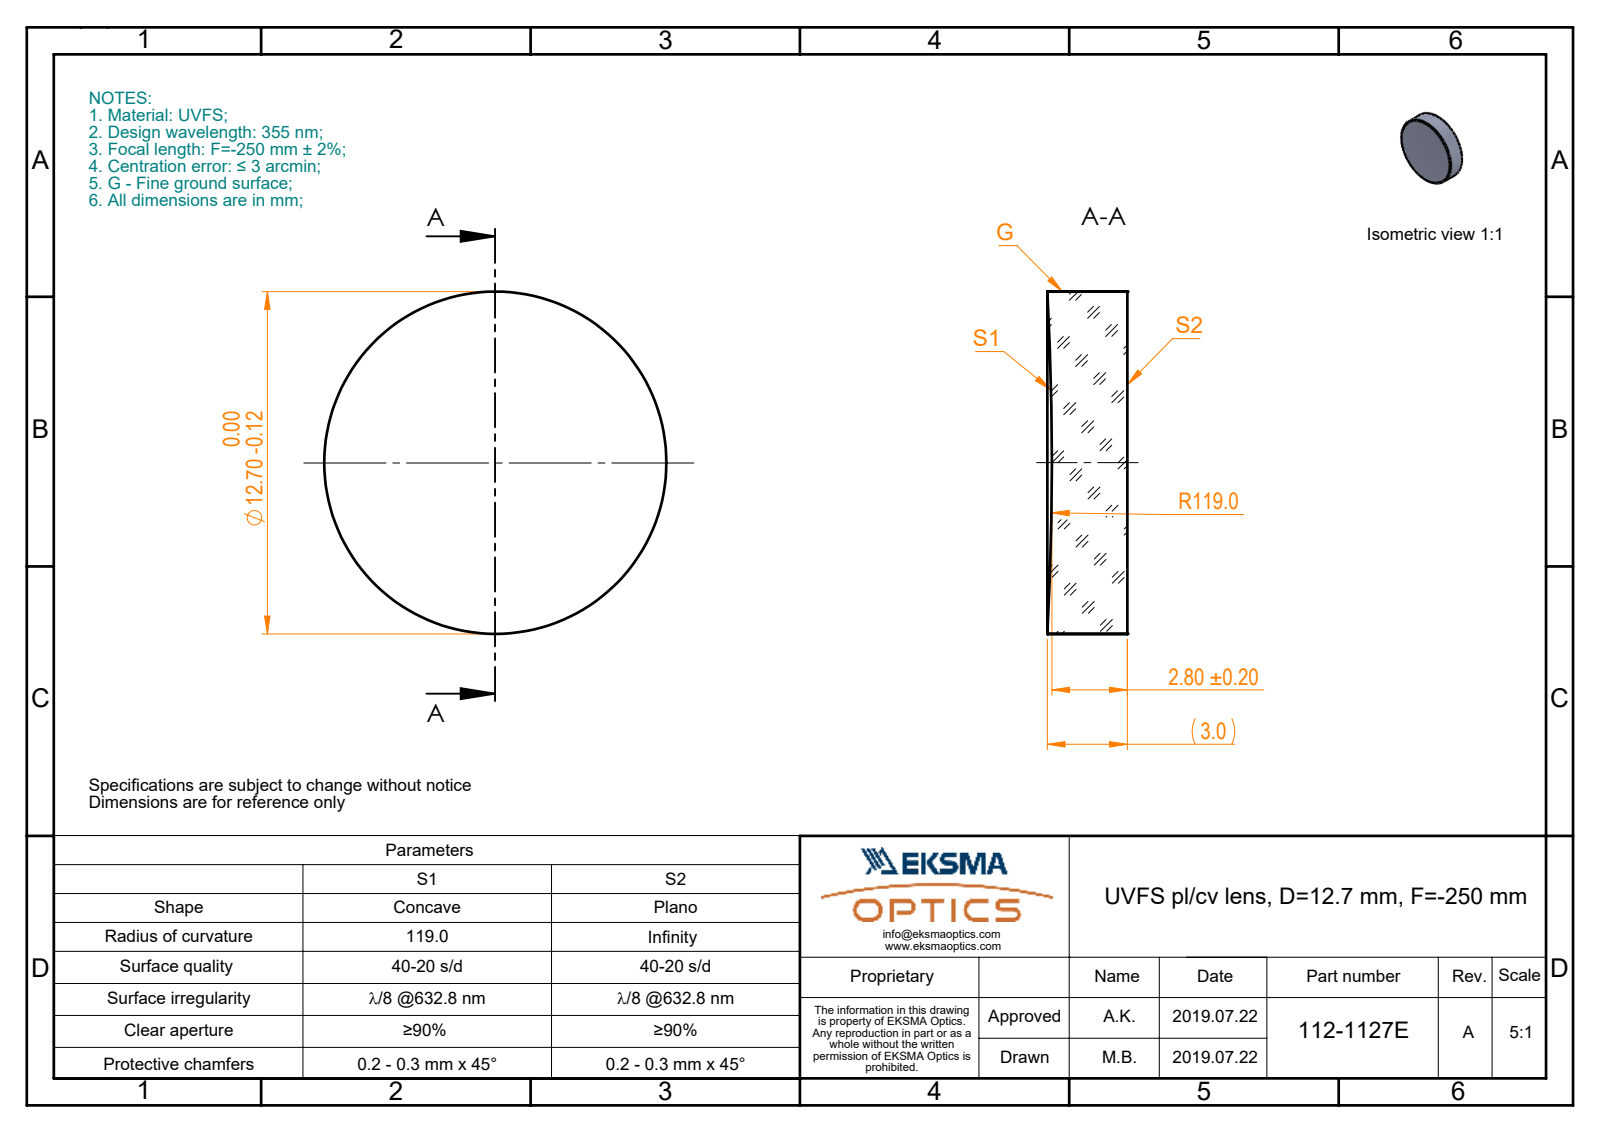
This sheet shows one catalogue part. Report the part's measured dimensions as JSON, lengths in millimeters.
{"part_name": "112-1127E UVFS pl-cv 12.7 F-250", "step_written_by": "SolidWorks 2017 (CONFIG_CONTROL_DESIGN)", "units": "millimeters", "bodies": {"solids": 1, "faces": 5, "planar": 1, "cylindrical": 2, "other": 2}, "overall_size": [12.7, 12.7, 2.97], "volume_mm3": 365, "surface_area_mm2": 372, "round_bosses_or_shafts": [[12.7, 1]]}
